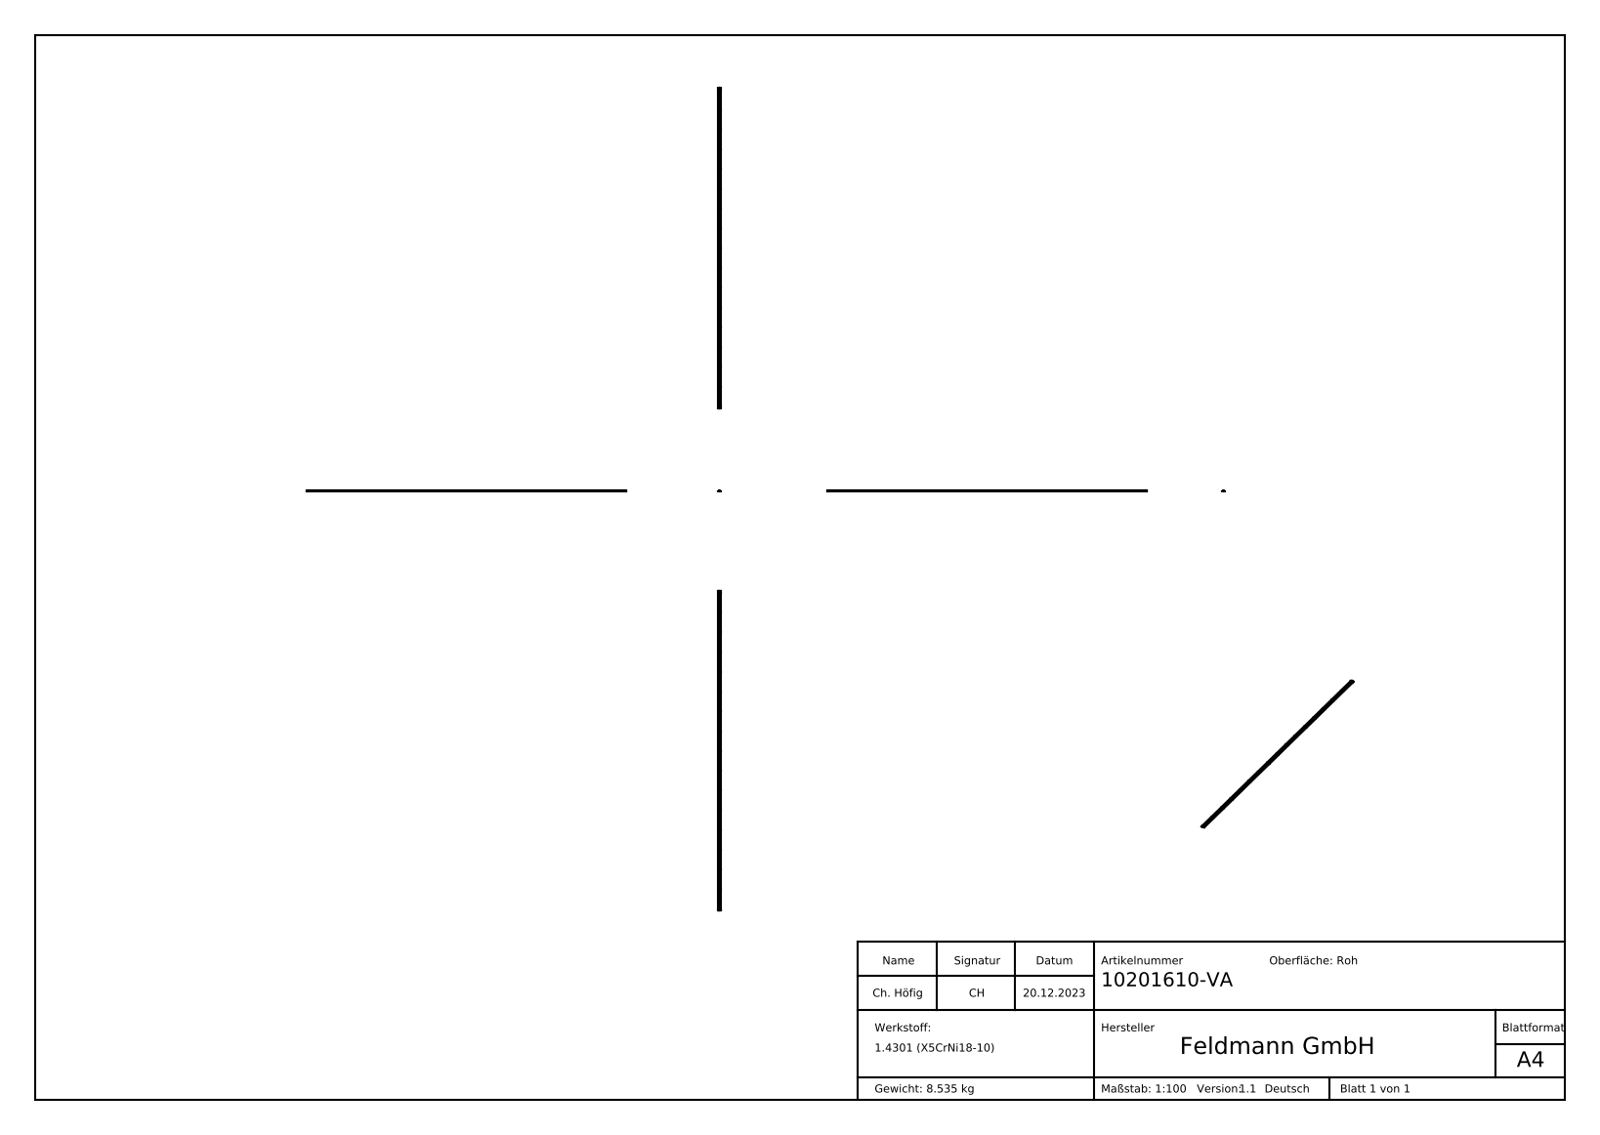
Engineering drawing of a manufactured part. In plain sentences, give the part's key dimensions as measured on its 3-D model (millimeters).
The part is named "10201610-VA". Its 3-D file was written by "SolidWorks 2018 (CONFIG_CONTROL_DESIGN)". It is 1 solid with 370 faces: 179 planar, 101 cylindrical and 90 other. Overall it measures 6000 by 58 by 15 millimeters. Its volume is 1 080 000 cubic millimeters and its surface area 896 683 square millimeters. Partial cylindrical surfaces (rounded edges, fillets, slot ends): 68 of radius 3.25, 2 of radius 3, 2 of radius 5.5, 1 of radius 7, 1 of radius 7.1, 1 of radius 9.5. The main face-to-face distances are 2.5, 58, 6000, 371.25, 742.5, 1113.75, 1485, 6.5, 377.75, 749.
